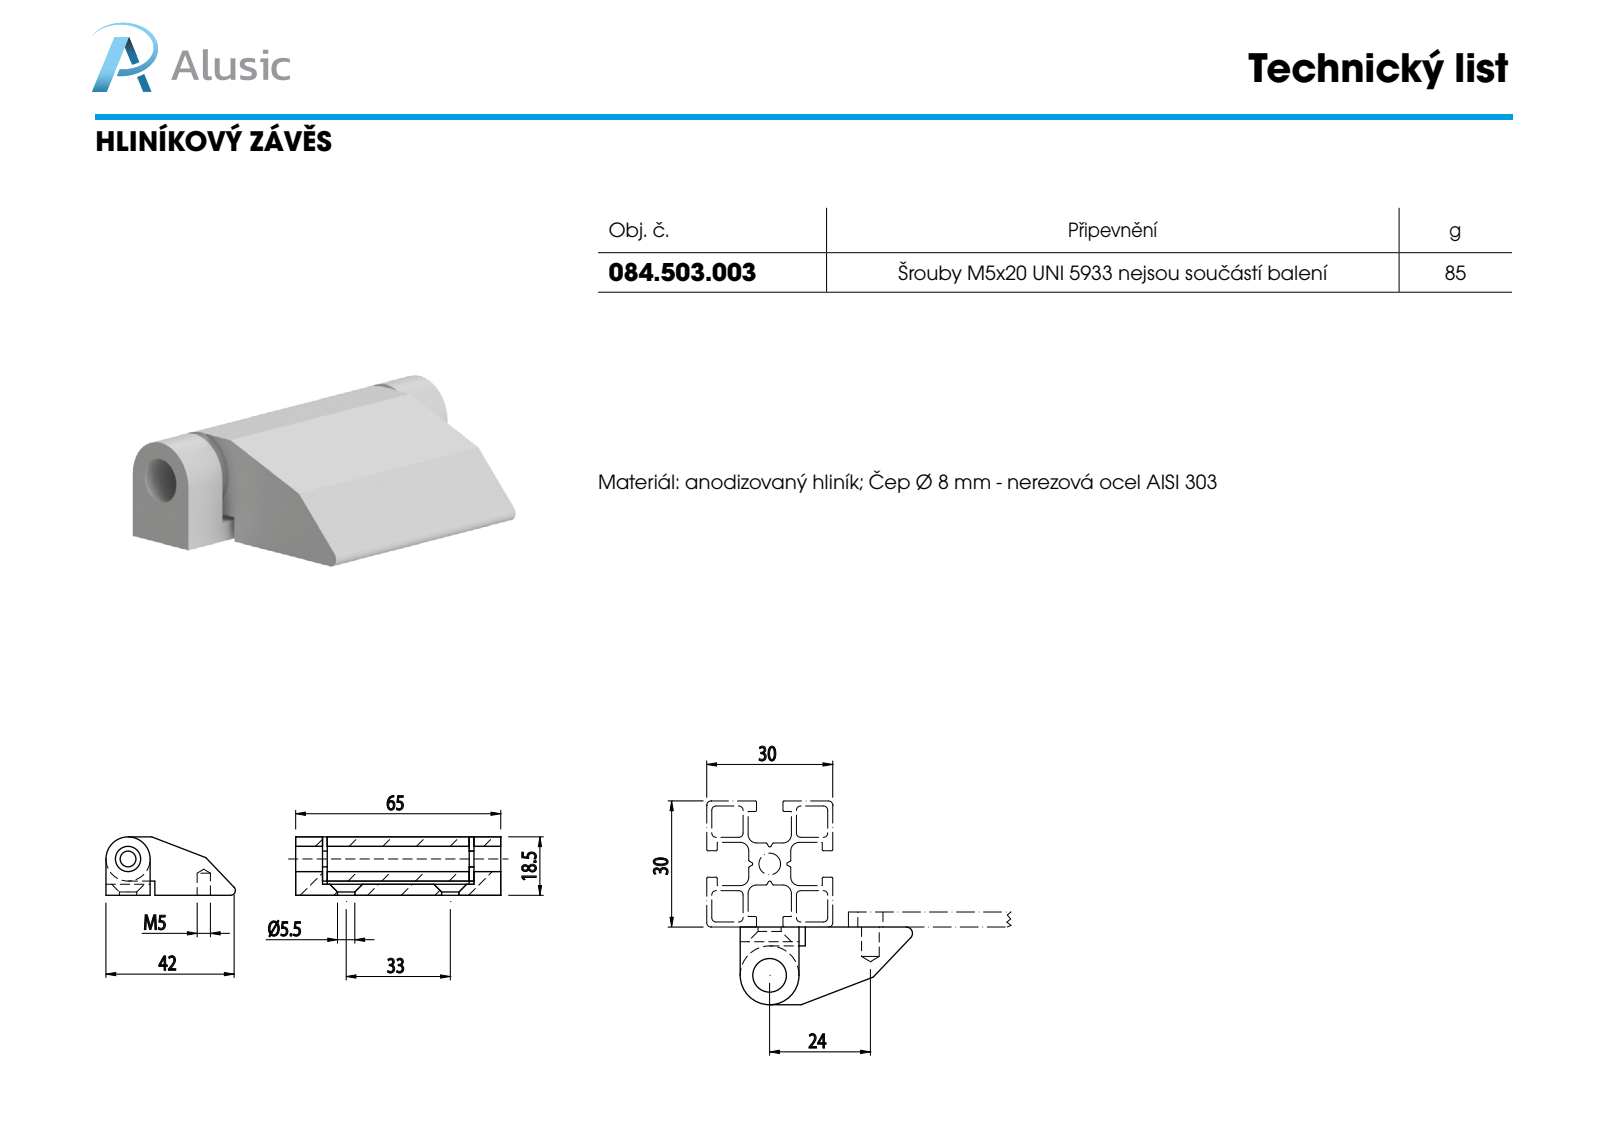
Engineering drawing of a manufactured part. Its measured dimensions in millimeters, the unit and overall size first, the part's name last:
Units: millimetres
Overall size (bounding box): 65 × 41.02 × 18.5
Round holes (diameter × count): ⌀4.2 ×2, ⌀5.5 ×2, ⌀8 ×1
Round bosses / shafts (diameter × count): ⌀14 ×1
Partial cylindrical surfaces — rounded edges, fillets, slot ends (radius × count): R1.5 ×1
Main face-to-face distances: 1.5, 14, 45, 46.5, 3.5, 4.5, 1, 8.5, 10, 55
Hole centre spacings: 24, 33, 40.8
Bodies: 0 solids, 45 faces (20 planar, 21 cylindrical, 4 other)
Part name (STEP PRODUCT): 084.503.003
STEP written by: SolidWorks 2012 (CONFIG_CONTROL_DESIGN)
